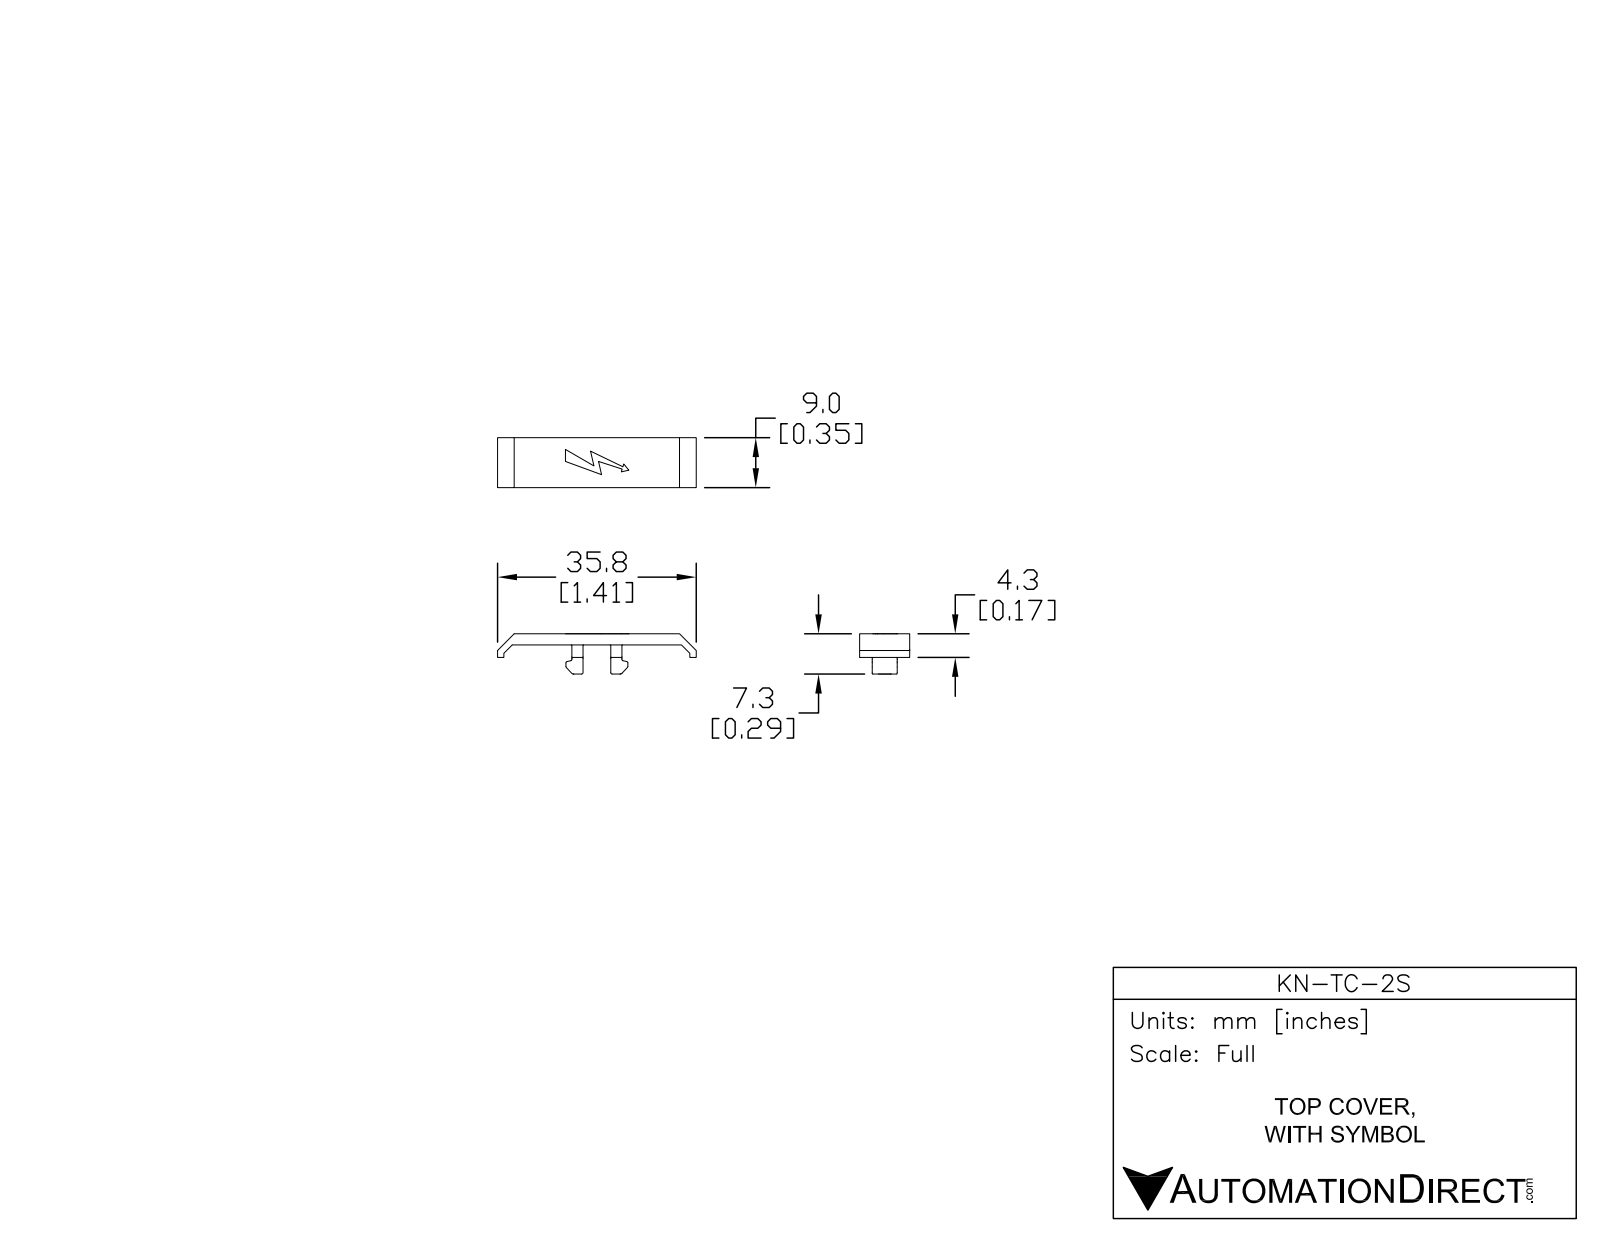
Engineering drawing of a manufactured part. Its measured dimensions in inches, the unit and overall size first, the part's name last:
Units: inches
Overall size (bounding box): 1.407 × 0.354 × 0.286
Partial cylindrical surfaces — rounded edges, fillets, slot ends (radius × count): R0.005 ×44, R0.01 ×8, R0.012 ×2, R0.02 ×2
Main face-to-face distances: 0.079, 0.354, 0.046, 0.089, 0.088, 0.266, 0.167, 0.167, 0.079, 0.197
Volume: 0.044 in³ · Surface area: 1.55 in²
Bodies: 1 solid, 166 faces (54 planar, 68 cylindrical, 44 other)
Part name (STEP PRODUCT): KN-TC-2S
STEP written by: SolidWorks 2014 (AUTOMOTIVE_DESIGN)
